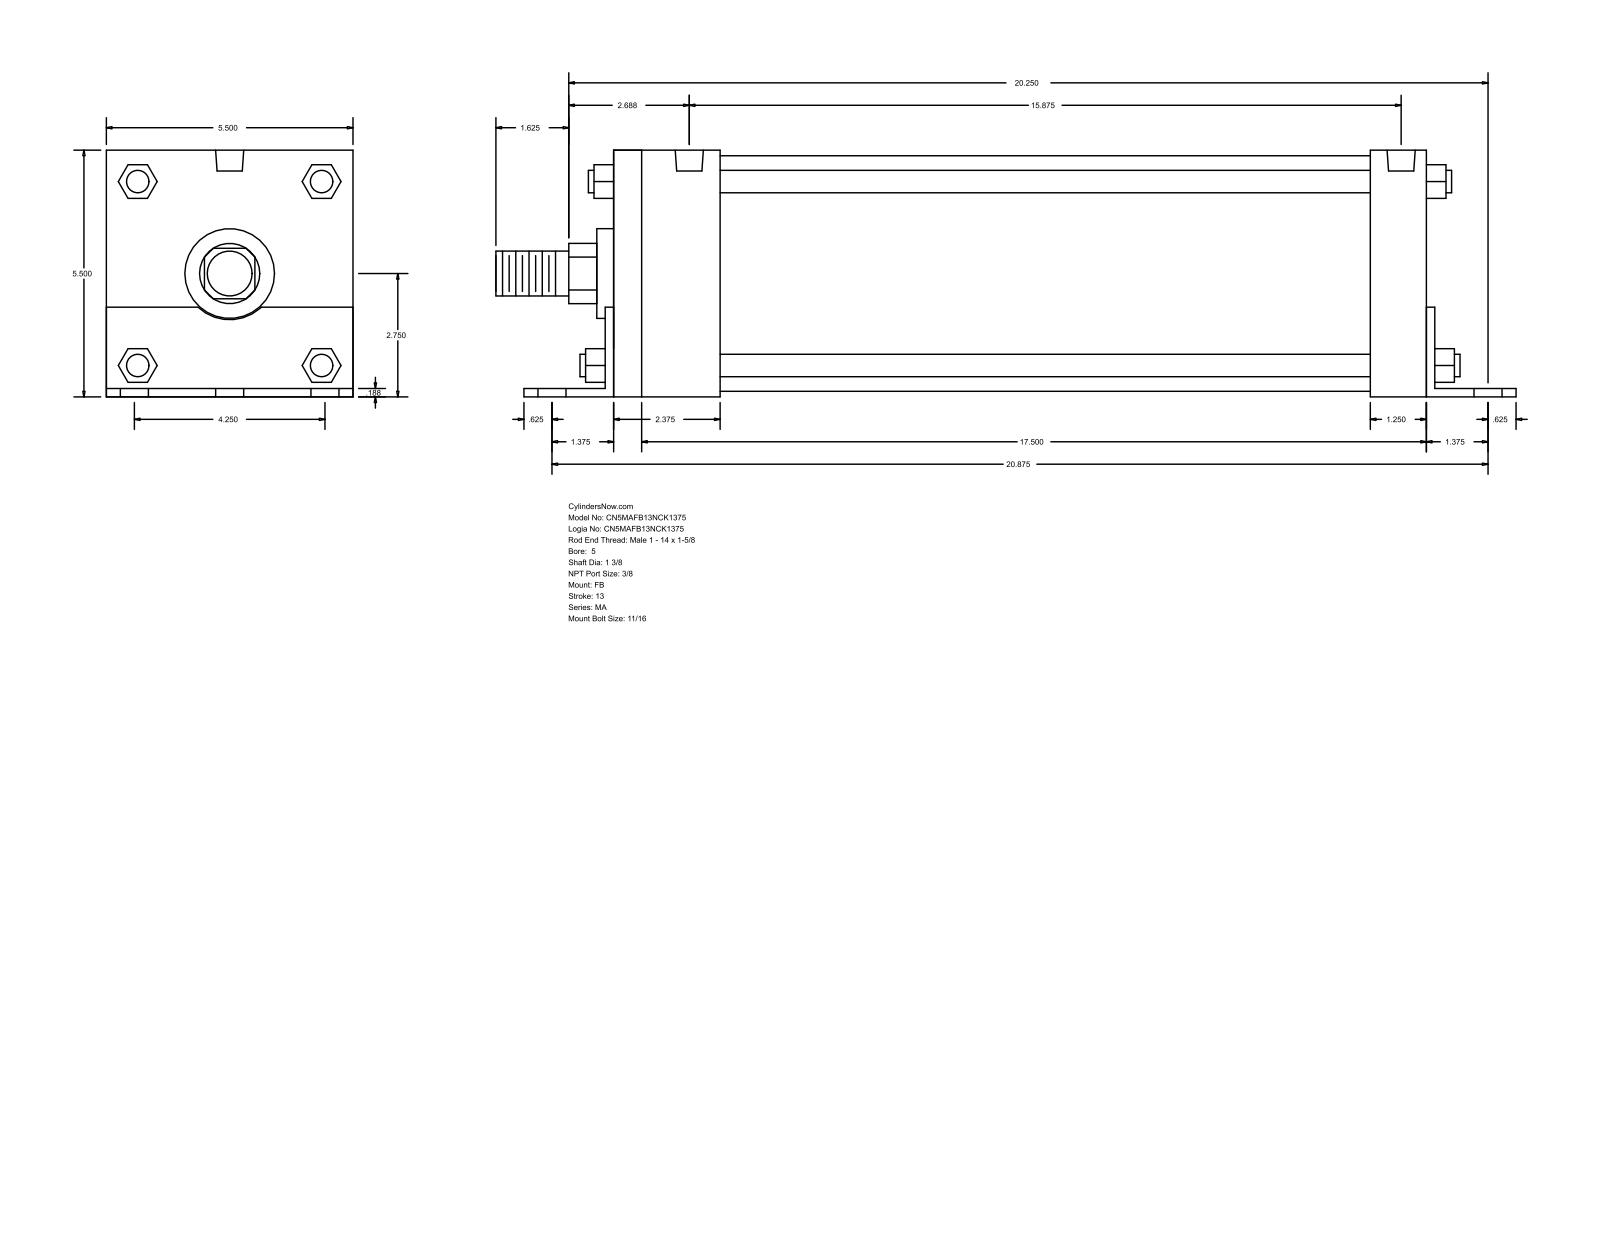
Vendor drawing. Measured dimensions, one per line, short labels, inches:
name: MA_FB__0500_1.375
written by: GSSL Pune (CONFIG_CONTROL_DESIGN)
unit: in
bodies: 0 solids, 140 faces (105 planar, 35 cylindrical, 0 other)
size: 22.75 × 5.502 × 5.5
holes: 6× ⌀0.687, 4× ⌀0.437, 2× ⌀0.627
bosses: 4× ⌀0.5, 1× ⌀5.25, 1× ⌀2, 1× ⌀1.375, 1× ⌀1
rounds: 1× R0.672, 1× R1.03
face distances: 5.5, 0.187, 5.502, 0.185, 5.315, 18.125, 0.188, 18.313, 18.312, 18.5
hole spacings: 2.125, 20.983, 20.875, 2.876, 3.005, 3.728, 3.883, 4.25
